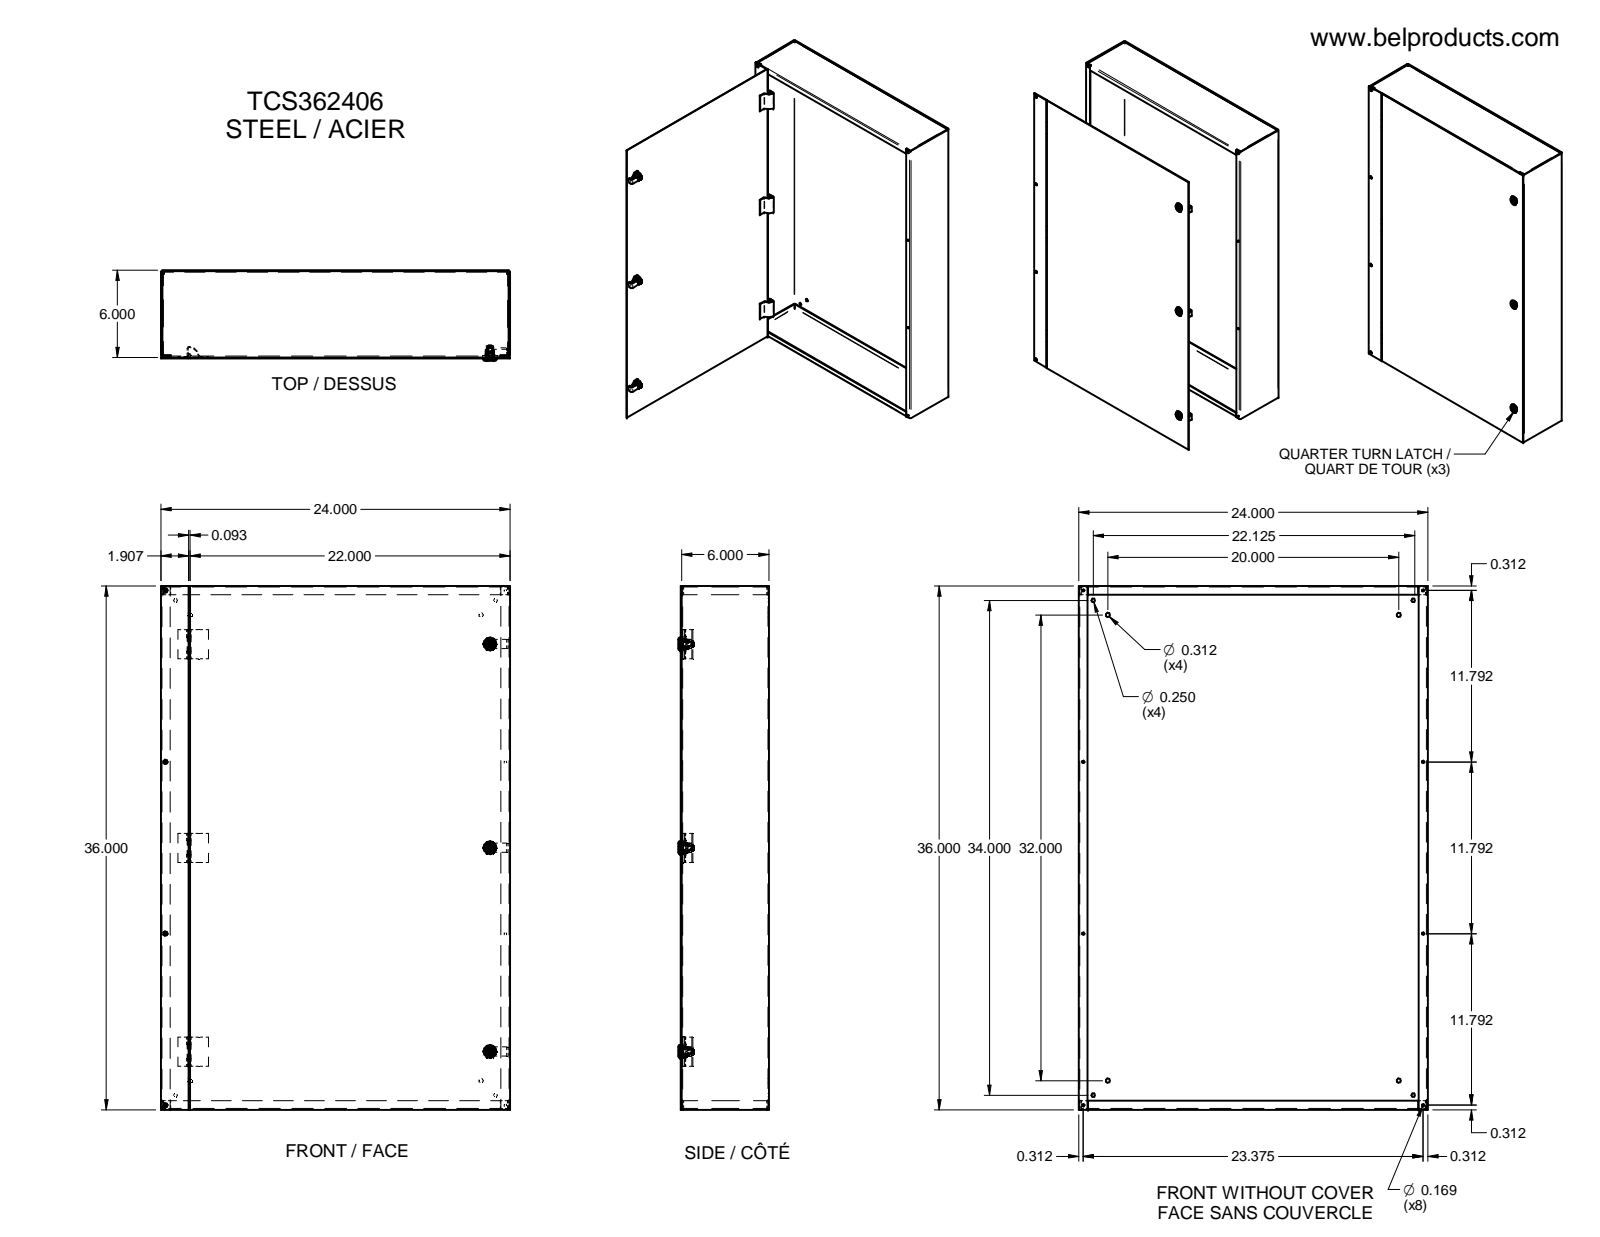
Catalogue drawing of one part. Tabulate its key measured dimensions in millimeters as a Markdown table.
| quantity | value |
| --- | --- |
| part name | LOCK AVEC TOURNEVIS TYPE 4-12 SANS CAME; HOSING-oa0; INSERT POUR TOURNEVIS-oa1; NOIX DE FIXATION-oa2 (+8 more) |
| STEP written by | Unknown (AUTOMOTIVE_DESIGN) |
| units | millimeters |
| bodies | 38 solids, 1559 faces (769 planar, 374 cylindrical, 416 other) |
| overall size | 914.4 × 609.6 × 158.78 |
| volume | 3 151 000 mm³ |
| surface area | 3 340 000 mm² |
| round holes (diameter × count) | 4.29 × 8, 7.92 × 8, 6.35 × 4, 6.99 × 3, 9.1 × 3, 11.18 × 3, 12.83 × 3, 15.8 × 3, 17.46 × 3, 3.81 × 1 |
| round bosses / shafts (diameter × count) | 22.86 × 3, 22.61 × 3, 15.75 × 3, 12.95 × 3, 12.62 × 3, 12.19 × 3, 11.86 × 3, 10.08 × 3 |
| partial cylindrical surfaces (radius × count) | 9.53 × 32, 0.25 × 24, 0.81 × 13, 2.72 × 12, 9.42 × 6, 6.22 × 3, 6.6 × 3, 6.99 × 3 |
| main face-to-face distances | 1.91, 152.4, 150.49, 154.31, 607.69, 1.9, 912.5, 609.6, 605.78, 914.4 |
| hole center spacings | 24.69, 35.92, 60.61, 260.2, 282.59, 299.51, 355.6, 534 |
